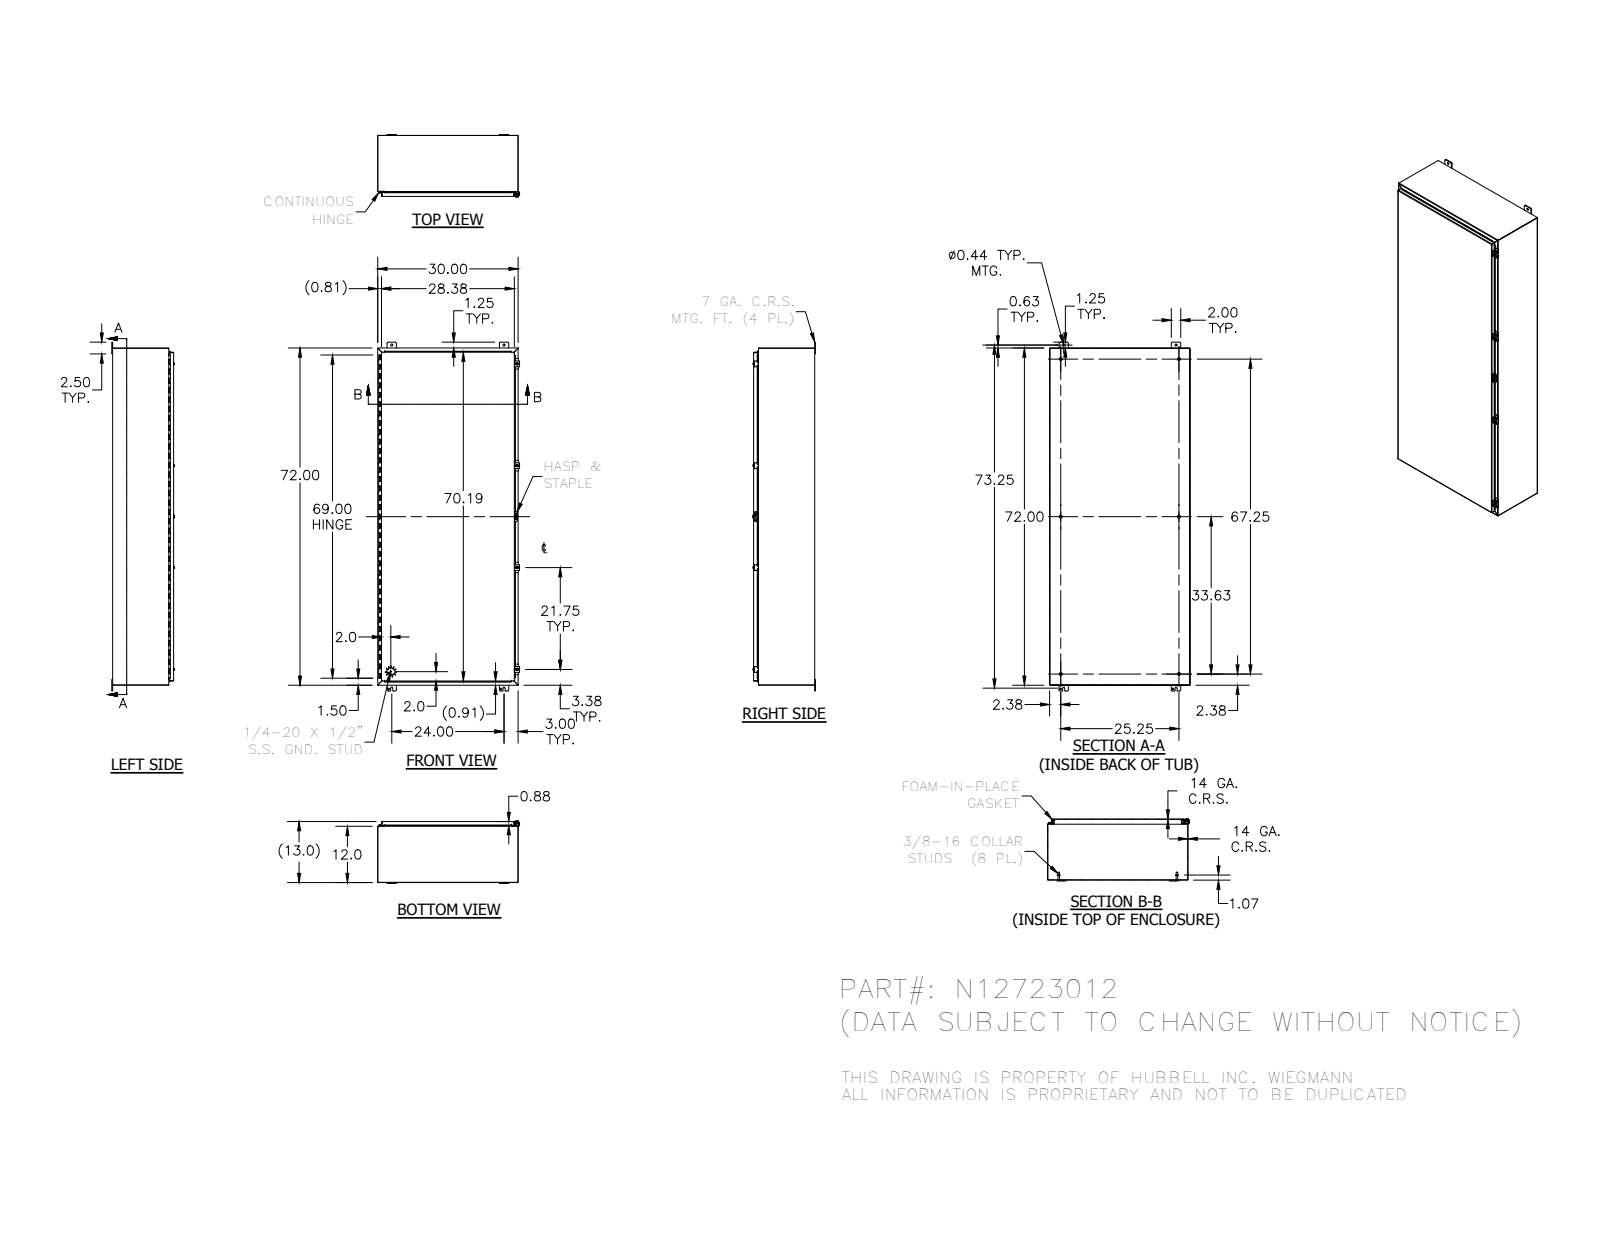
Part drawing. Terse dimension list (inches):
name: N12723012; 34840; 38413; N123012TB (+8 more)
written by: Autodesk Inventor 2012 (AUTOMOTIVE_DESIGN)
unit: in
bodies: 41 solids, 1564 faces (927 planar, 496 cylindrical, 141 other)
size: 74.5 × 30.311 × 13.41
volume: 569.1 in³; area: 15 118 in²
holes: 4× ⌀0.211, 4× ⌀0.281, 4× ⌀0.3, 4× ⌀0.313, 4× ⌀0.438, 3× ⌀0.11, 1× ⌀0.125, 1× ⌀0.156, 1× ⌀0.5
bosses: 6× ⌀0.625, 6× ⌀0.33, 6× ⌀0.25, 4× ⌀0.52, 4× ⌀0.5, 4× ⌀0.35, 1× ⌀0.337, 1× ⌀0.12
rounds: 51× R0.03, 29× R0.125, 29× R0.25, 21× R0.031, 21× R0.105, 17× R0.063, 8× R0.1, 8× R0.141
face distances: 0.074, 12.959, 12.885, 13.033, 29.926, 30, 29.852, 71.926, 11.926, 1.033
hole spacings: 1.593, 24, 72, 75.894, 21.75, 0.791, 23.357, 24.729
